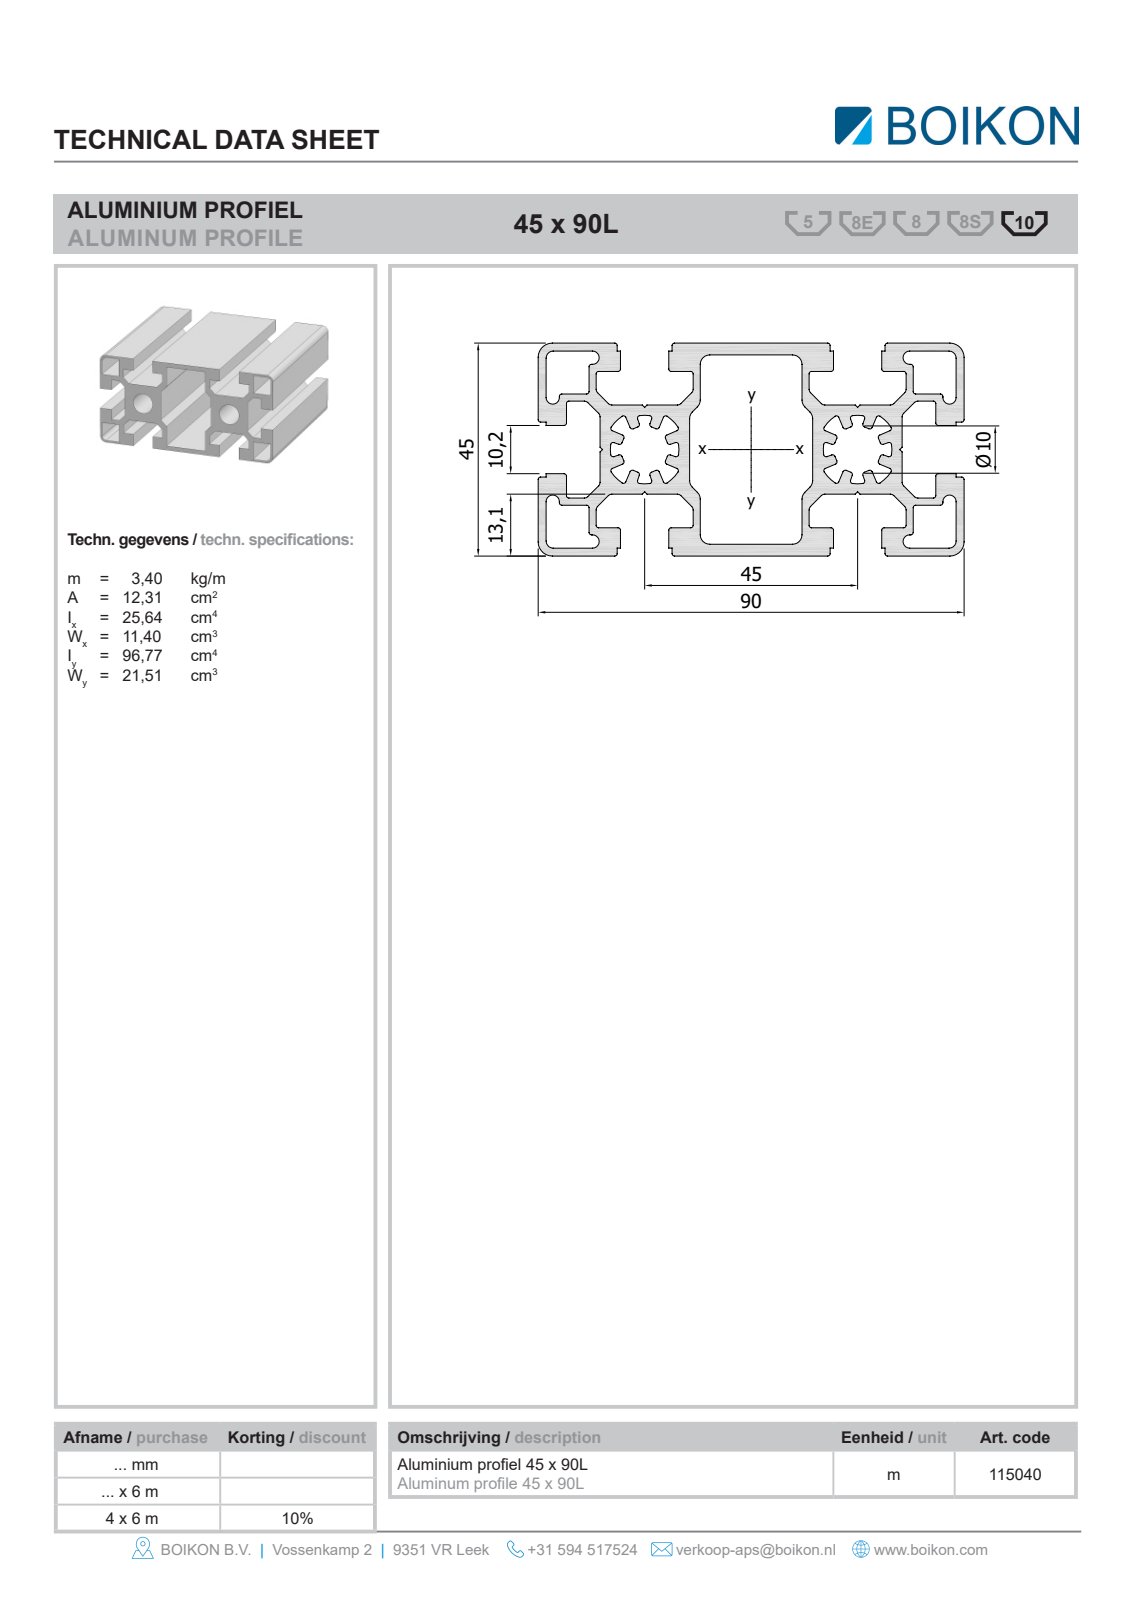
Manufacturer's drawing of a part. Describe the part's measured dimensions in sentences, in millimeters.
The part is named "Root; 11504045x90LBOIKON0". Its 3-D file was written by "HiCAD 2013 1802.4 Build 509 (AUTOMOTIVE_DESIGN)". It is 1 solid with 104 faces: 94 planar, 10 cylindrical and 0 other. Overall it measures 1000 by 90 by 45 millimeters. Its volume is 1 441 000 cubic millimeters and its surface area 859 252 square millimeters. Round holes: 2 of diameter 10.2. Partial cylindrical surfaces (rounded edges, fillets, slot ends): 4 of radius 2, 4 of radius 3. The main face-to-face distances are 45, 13.1, 31.9, 10, 14.5, 4.3, 3.1, 21.9, 6, 7.1. The hole center spacings are 45.
